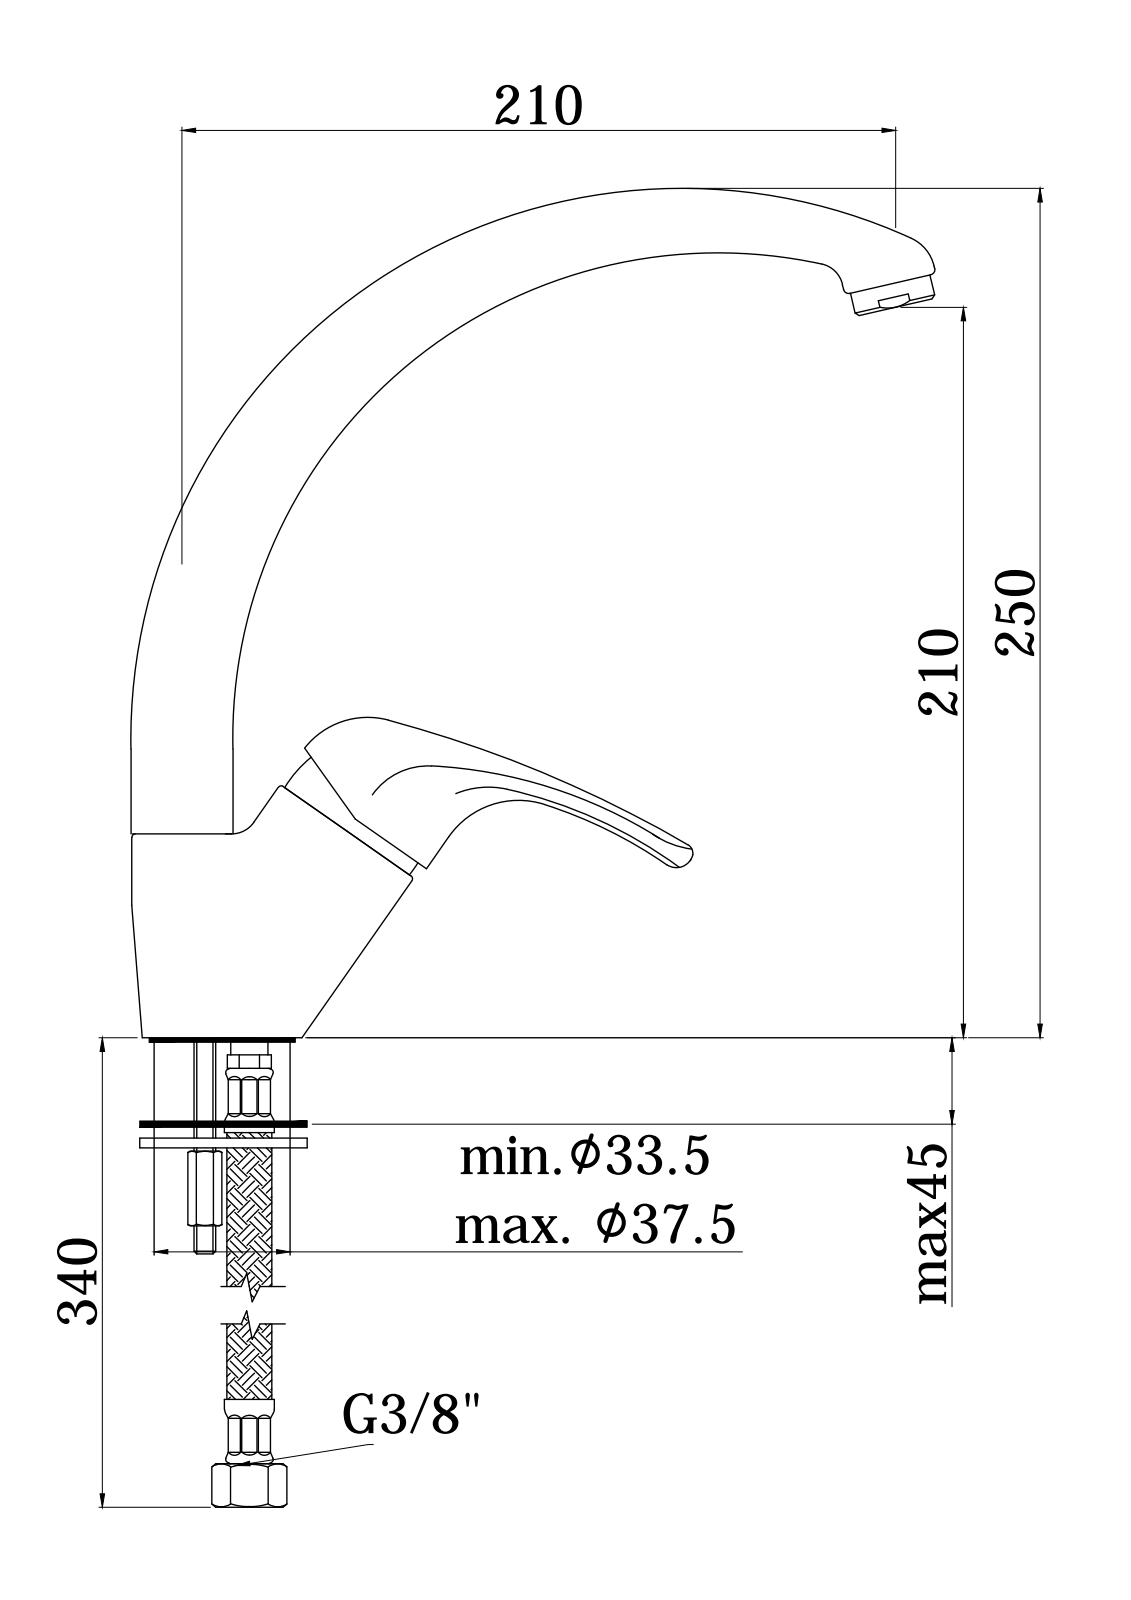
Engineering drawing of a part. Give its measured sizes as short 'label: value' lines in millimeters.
name: ND181CR
written by: CREO PARAMETRIC BY PTC INC, 2020044 (CONFIG_CONTROL_DESIGN)
unit: mm
bodies: 1 solid, 315 faces (90 planar, 90 cylindrical, 135 other)
size: 251.6 × 246.02 × 170.44
volume: 348 621 mm³; area: 78 717 mm²
holes: 3× ⌀8, 2× ⌀5, 2× ⌀5.5, 2× ⌀6, 2× ⌀9, 2× ⌀11, 2× ⌀42.5, 1× ⌀3, 1× ⌀4, 1× ⌀16, 1× ⌀17, 1× ⌀17.3
bosses: 1× ⌀37, 1× ⌀24, 1× ⌀20, 1× ⌀7.6, 1× ⌀5.5, 1× ⌀5
rounds: 2× R1.5, 1× R3.9, 1× R4
face distances: 60.87, 60.9, 56.6, 3, 1.5, 55.1, 53.6, 15.31, 0.7, 52.1
hole spacings: 8.6, 9.92, 12.78, 13.46, 13.9, 15, 15.62, 15.81
